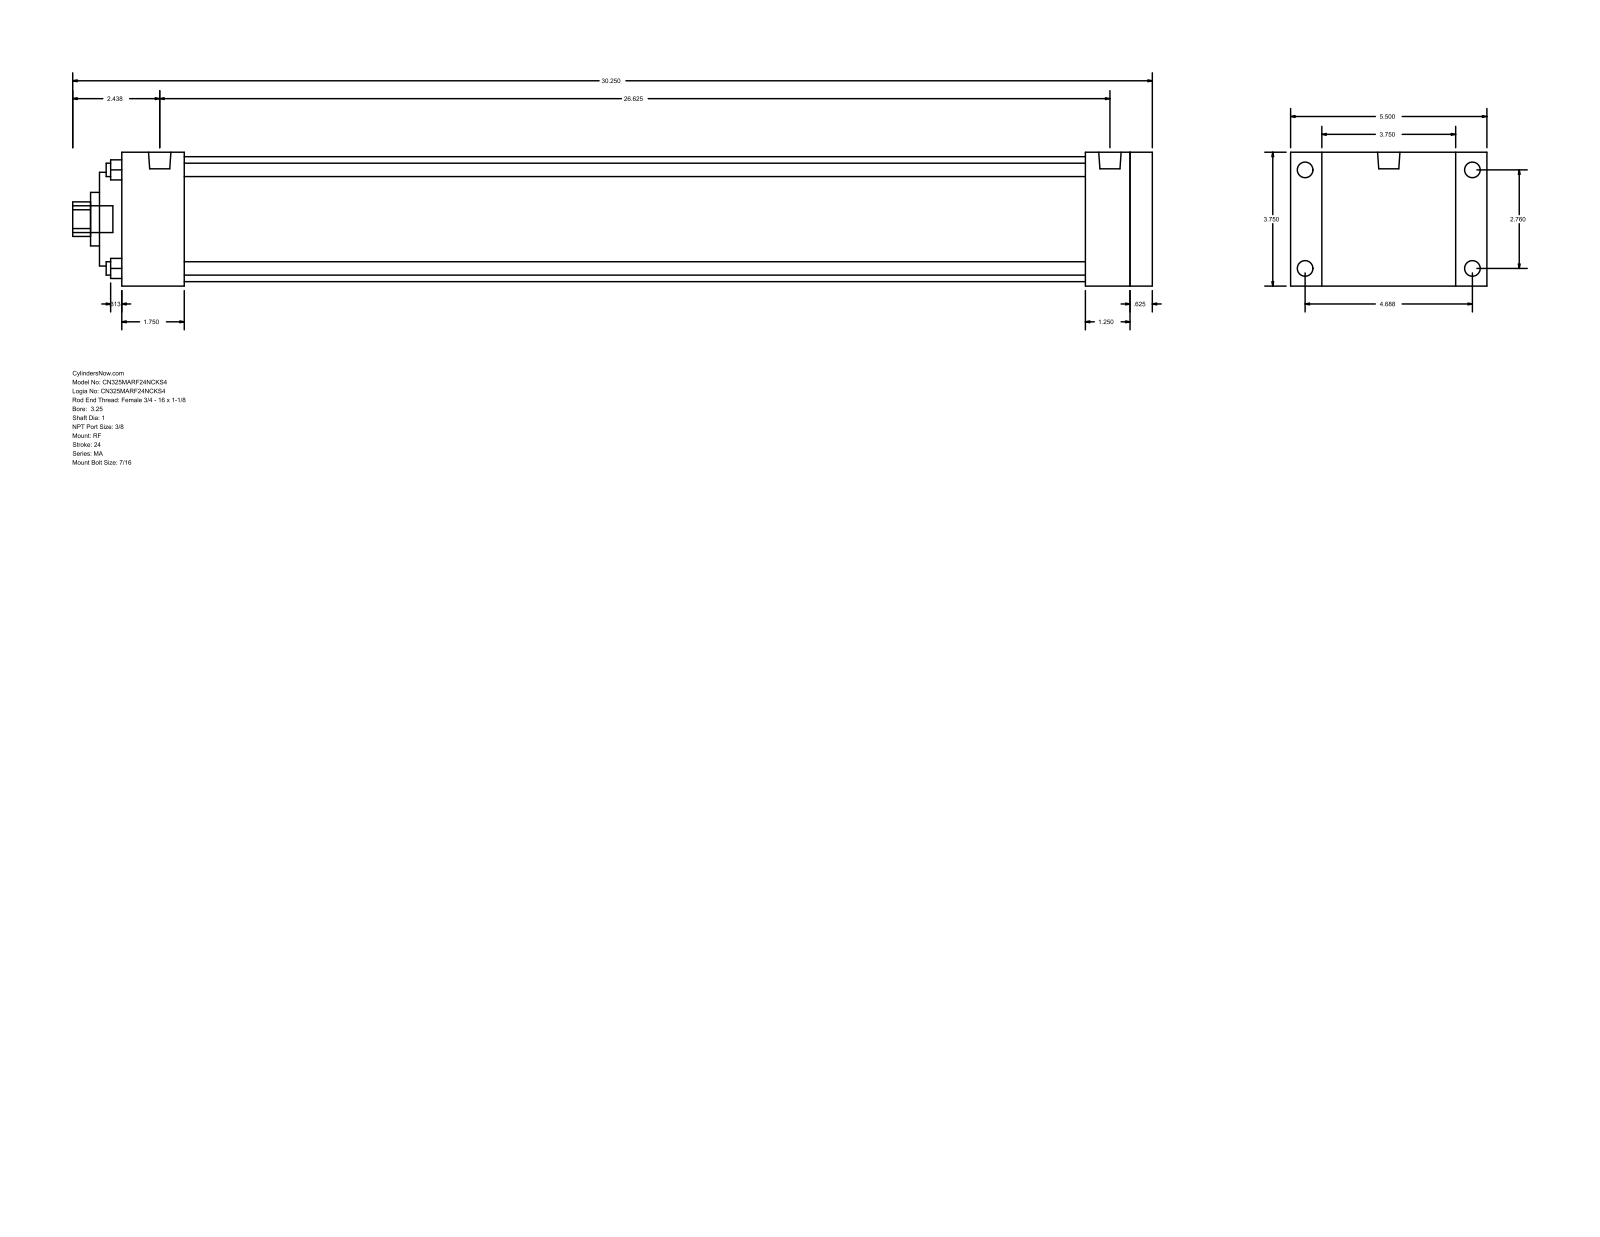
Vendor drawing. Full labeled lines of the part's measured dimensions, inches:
Part name (STEP PRODUCT): MA_RF__0325_1
STEP written by: GSSL Pune (CONFIG_CONTROL_DESIGN)
Units: inches
Bodies: 0 solids, 94 faces (65 planar, 29 cylindrical, 0 other)
Overall size (bounding box): 30.25 × 5.5 × 3.75
Round holes (diameter × count): ⌀0.375 ×4, ⌀1 ×1, ⌀1.5 ×1, ⌀2.625 ×1, ⌀3.5 ×1
Round bosses / shafts (diameter × count): ⌀0.437 ×8, ⌀0.627 ×2, ⌀0.75 ×1
Partial cylindrical surfaces — rounded edges, fillets, slot ends (radius × count): R0.484 ×1
Main face-to-face distances: 3.75, 28.875, 0.625, 28.25, 0.875, 4.625, 27, 1.25, 1.875, 1.75
Hole centre spacings: 1.952, 2.76, 3.903
